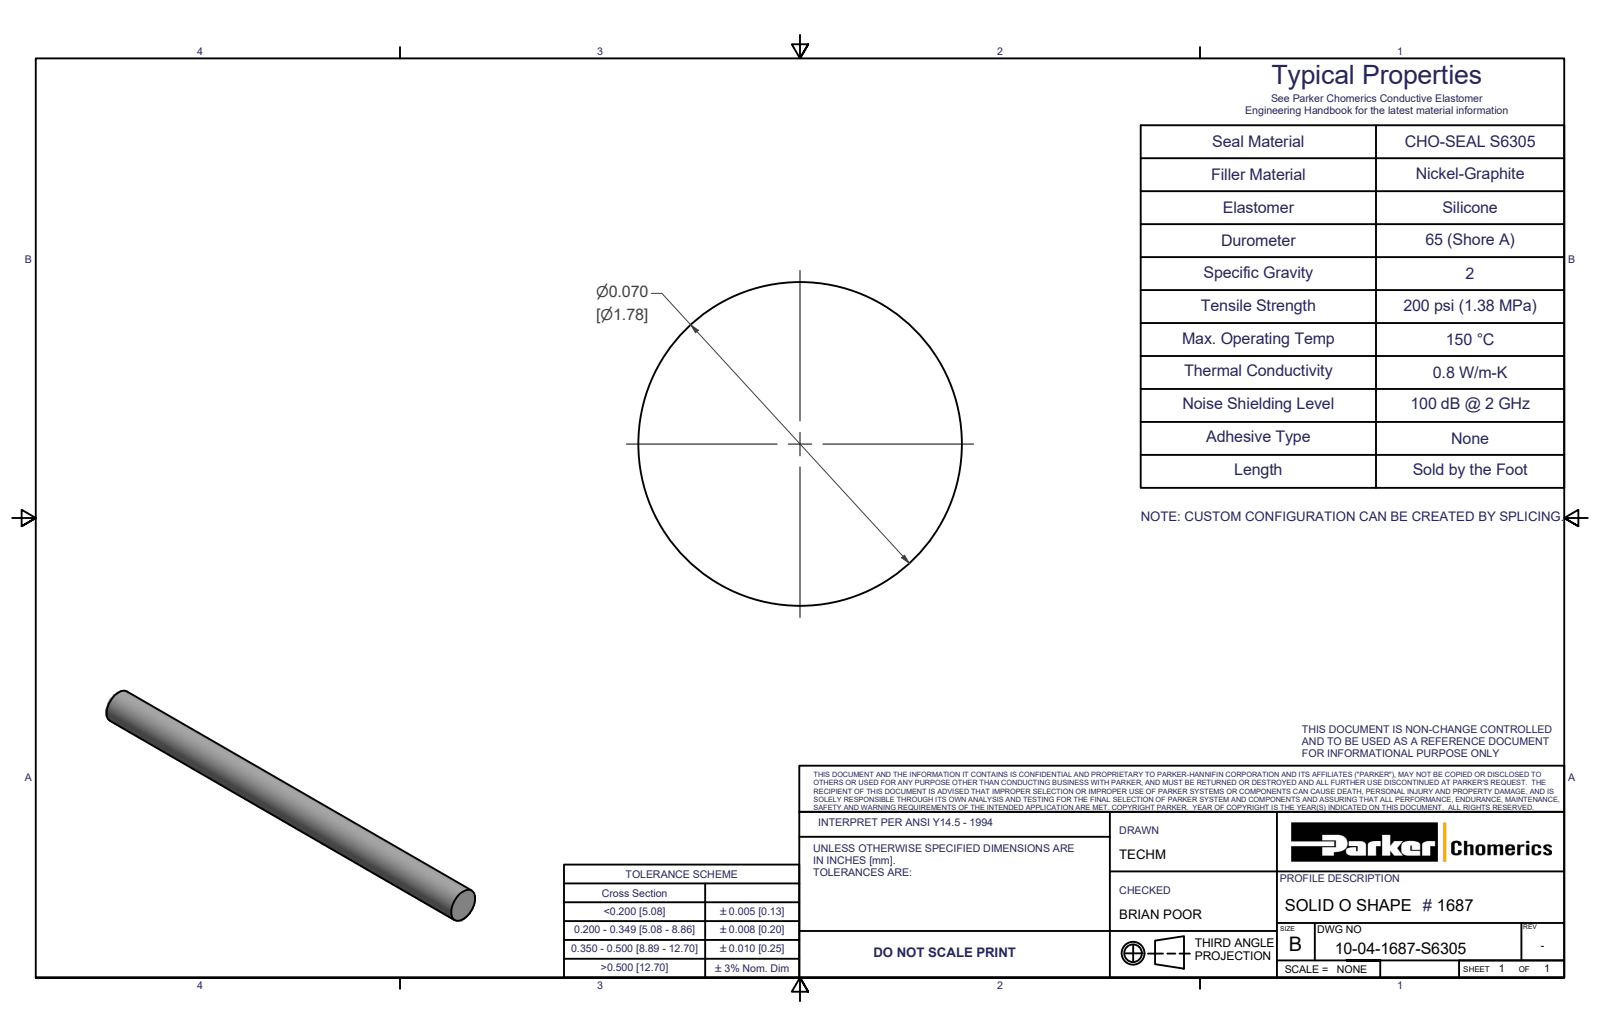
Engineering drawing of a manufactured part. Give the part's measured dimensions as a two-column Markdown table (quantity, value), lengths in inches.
| quantity | value |
| --- | --- |
| part name | 10-04-1687-S6305 |
| STEP written by | Autodesk Inventor 2020 (AUTOMOTIVE_DESIGN) |
| units | inches |
| bodies | 1 solid, 3 faces (2 planar, 1 cylindrical, 0 other) |
| overall size | 1 × 0.07 × 0.07 |
| volume | 0.004 in³ |
| surface area | 0.228 in² |
| round bosses / shafts (diameter × count) | 0.07 × 1 |
| main face-to-face distances | 1 |
